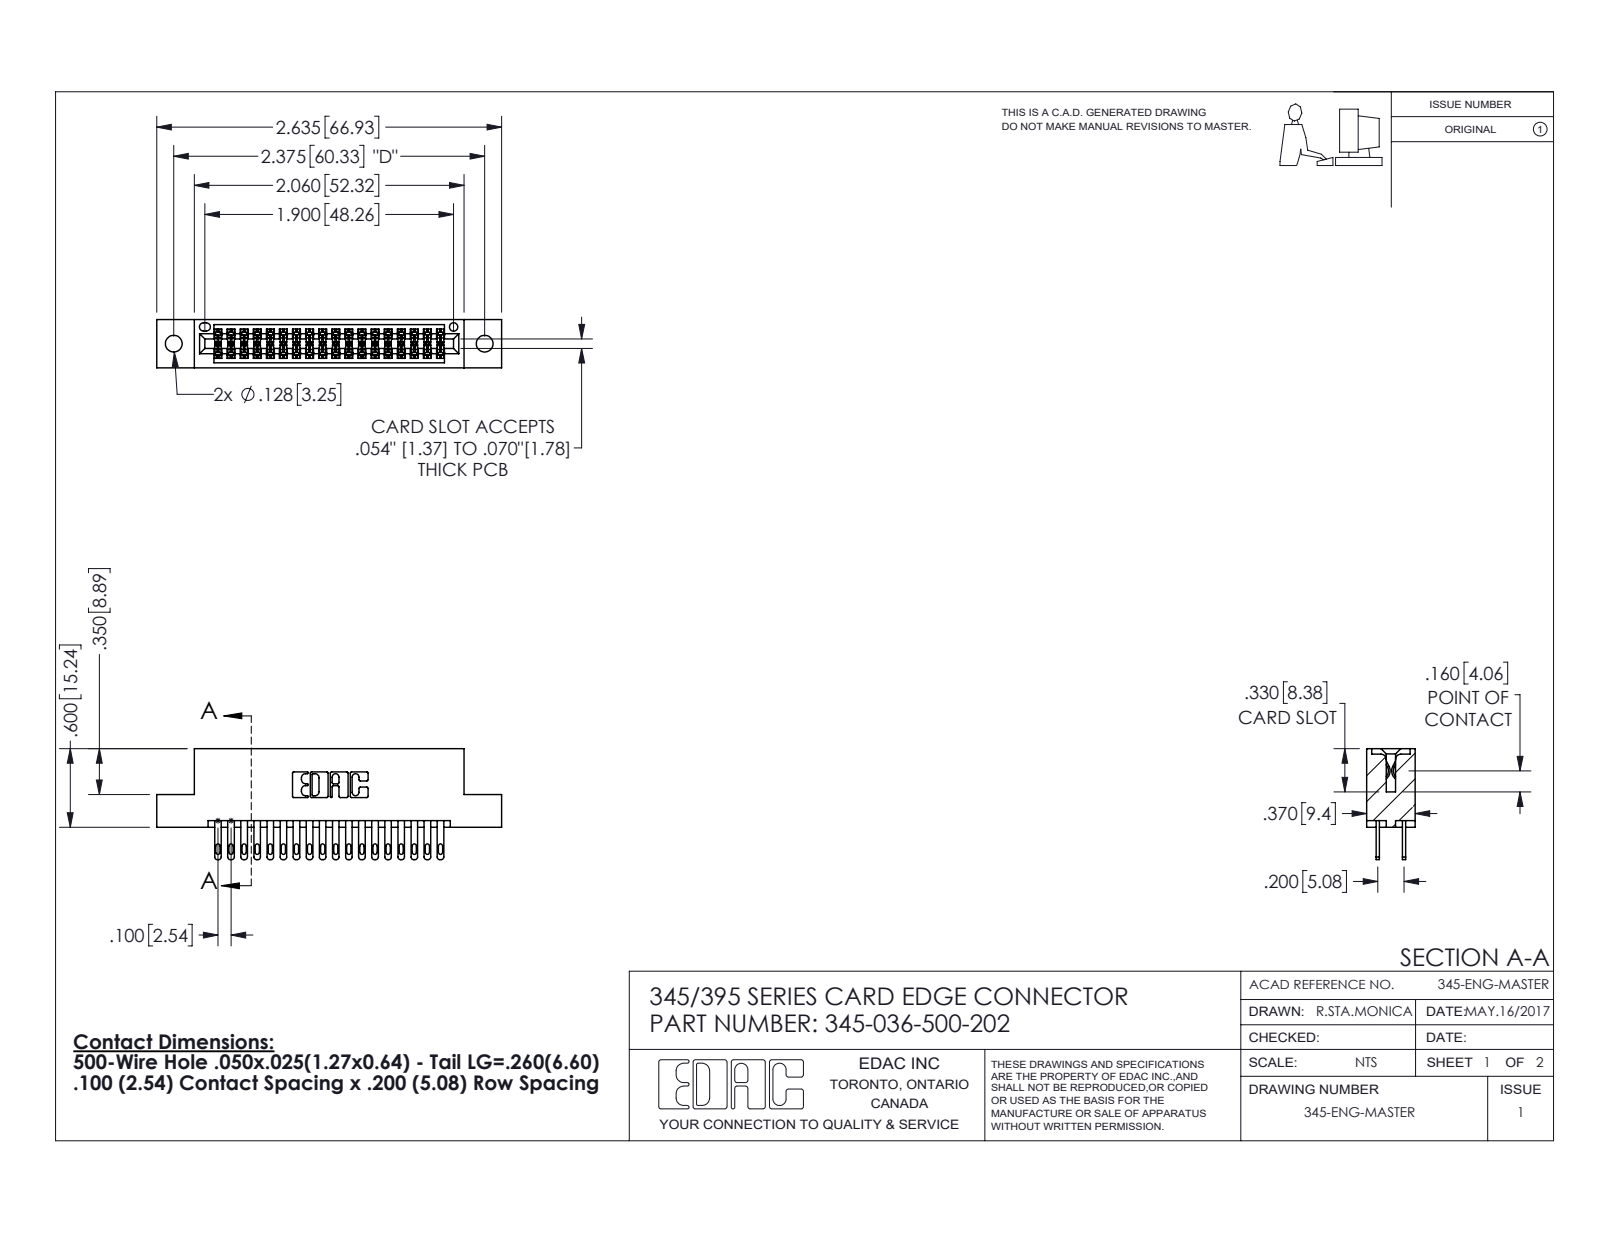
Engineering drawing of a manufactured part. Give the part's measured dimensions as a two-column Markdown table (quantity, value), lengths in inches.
| quantity | value |
| --- | --- |
| part name | 345-292-001_345-293-100; 345 Part_Flush Mounting Lugs - 0.128 Dia; 345-036-500-202 |
| STEP written by | SolidWorks 2016 (CONFIG_CONTROL_DESIGN) |
| units | inches |
| bodies | 37 solids, 1782 faces (1052 planar, 730 cylindrical, 0 other) |
| overall size | 2.635 × 0.847 × 0.37 |
| volume | 0.388 in³ |
| surface area | 13.98 in² |
| round holes (diameter × count) | 0.128 × 2, 0.064 × 1 |
| partial cylindrical surfaces (radius × count) | 0.006 × 54, 0.016 × 36, 0.02 × 36, 0.01 × 22, 0.007 × 6, 0.031 × 6, 0.026 × 3, 0.014 × 2 |
| main face-to-face distances | 0.298, 0.072, 0.2, 0.098, 0.272, 0.025, 0.37, 0.225, 0.175, 0.1 |
| hole center spacings | 0.27, 2.141, 2.375 |
